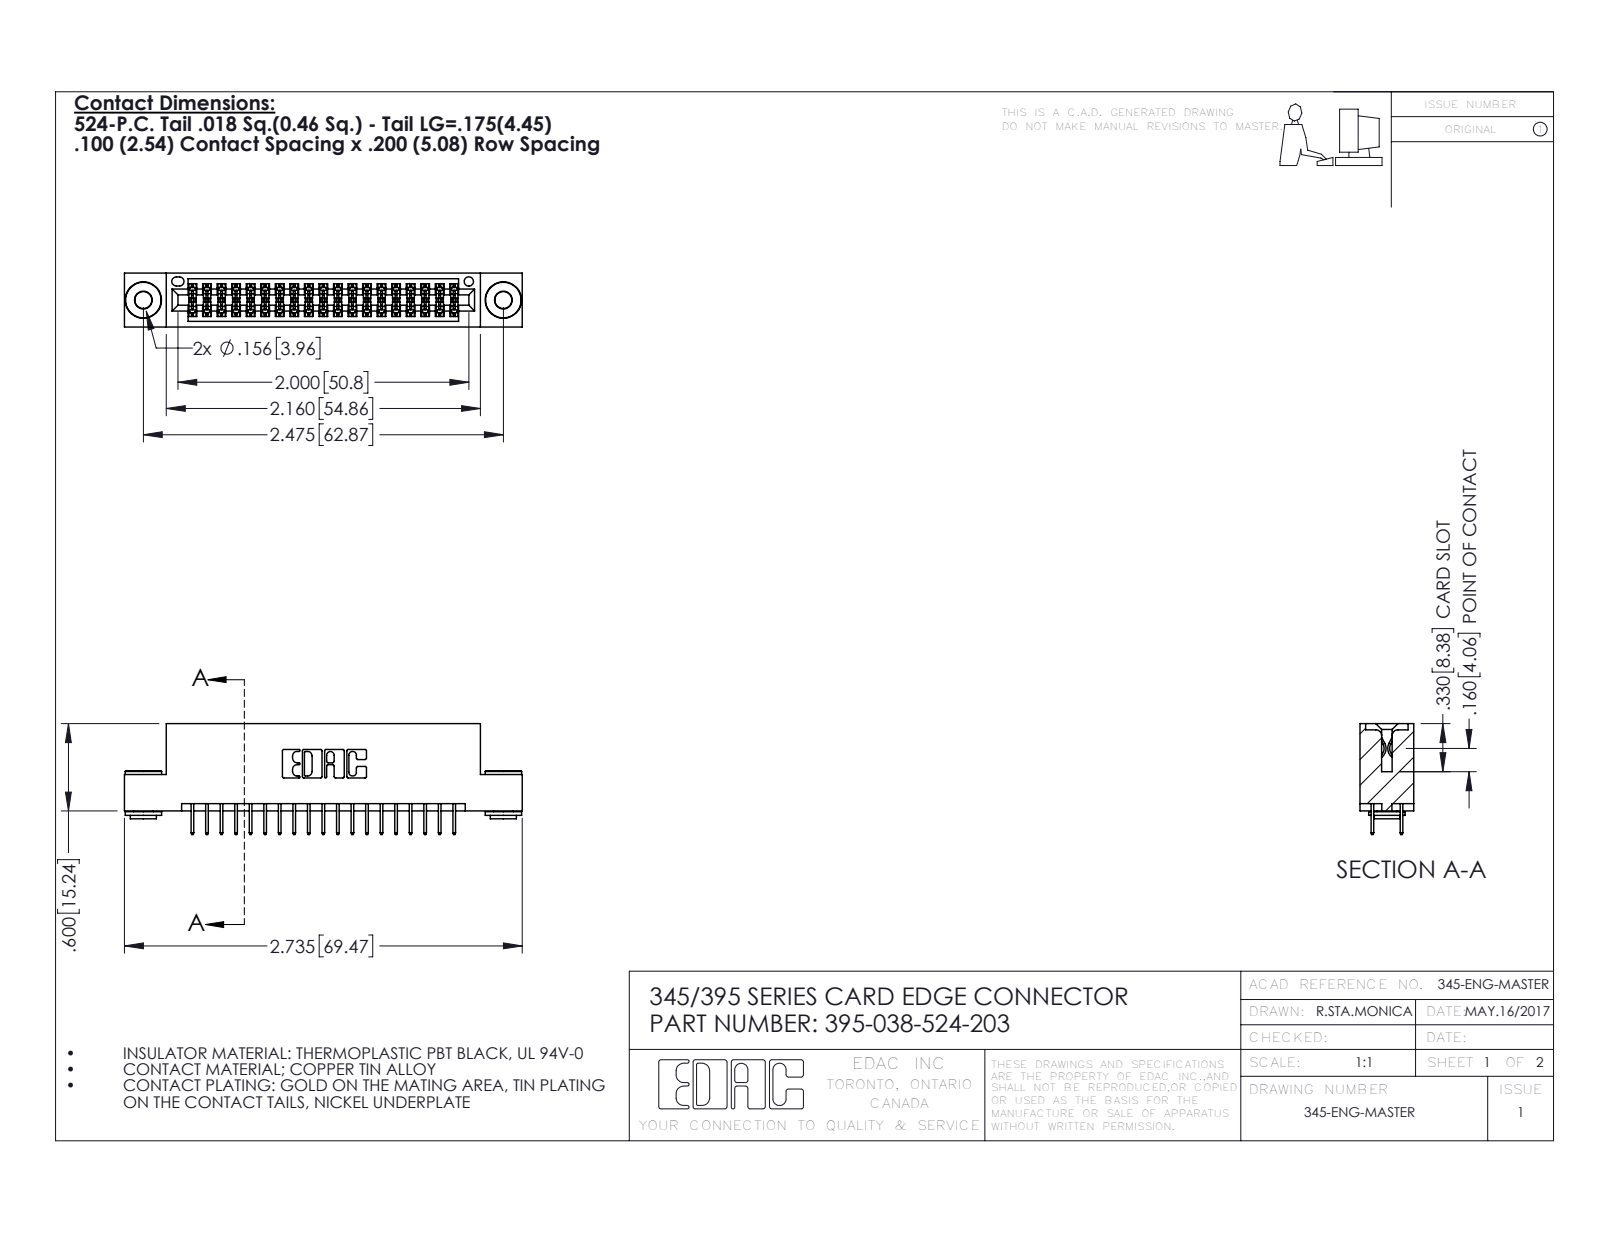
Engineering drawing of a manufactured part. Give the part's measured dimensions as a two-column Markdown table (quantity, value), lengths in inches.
| quantity | value |
| --- | --- |
| part name | 345-250-002_345-250-002-102; 345 Part_Flush Mounting Lugs - 0.156 Dia-TH; 395-038-524-203; 345-292-001_345-293-124 |
| STEP written by | SolidWorks 2016 (CONFIG_CONTROL_DESIGN) |
| units | inches |
| bodies | 41 solids, 2216 faces (1572 planar, 636 cylindrical, 8 other) |
| overall size | 2.735 × 0.762 × 0.37 |
| volume | 0.396 in³ |
| surface area | 14.28 in² |
| round holes (diameter × count) | 0.116 × 2, 0.156 × 2, 0.064 × 1 |
| round bosses / shafts (diameter × count) | 0.25 × 2, 0.18 × 2, 0.136 × 2 |
| partial cylindrical surfaces (radius × count) | 0.006 × 57, 0.01 × 22, 0.007 × 6, 0.031 × 6, 0.026 × 3, 0.014 × 2, 0.019 × 2, 0.022 × 2 |
| main face-to-face distances | 0.2, 0.072, 0.298, 0.37, 0.025, 0.098, 0.272, 0.225, 0.072, 0.175 |
| hole center spacings | 0.27, 2.241, 2.475 |
